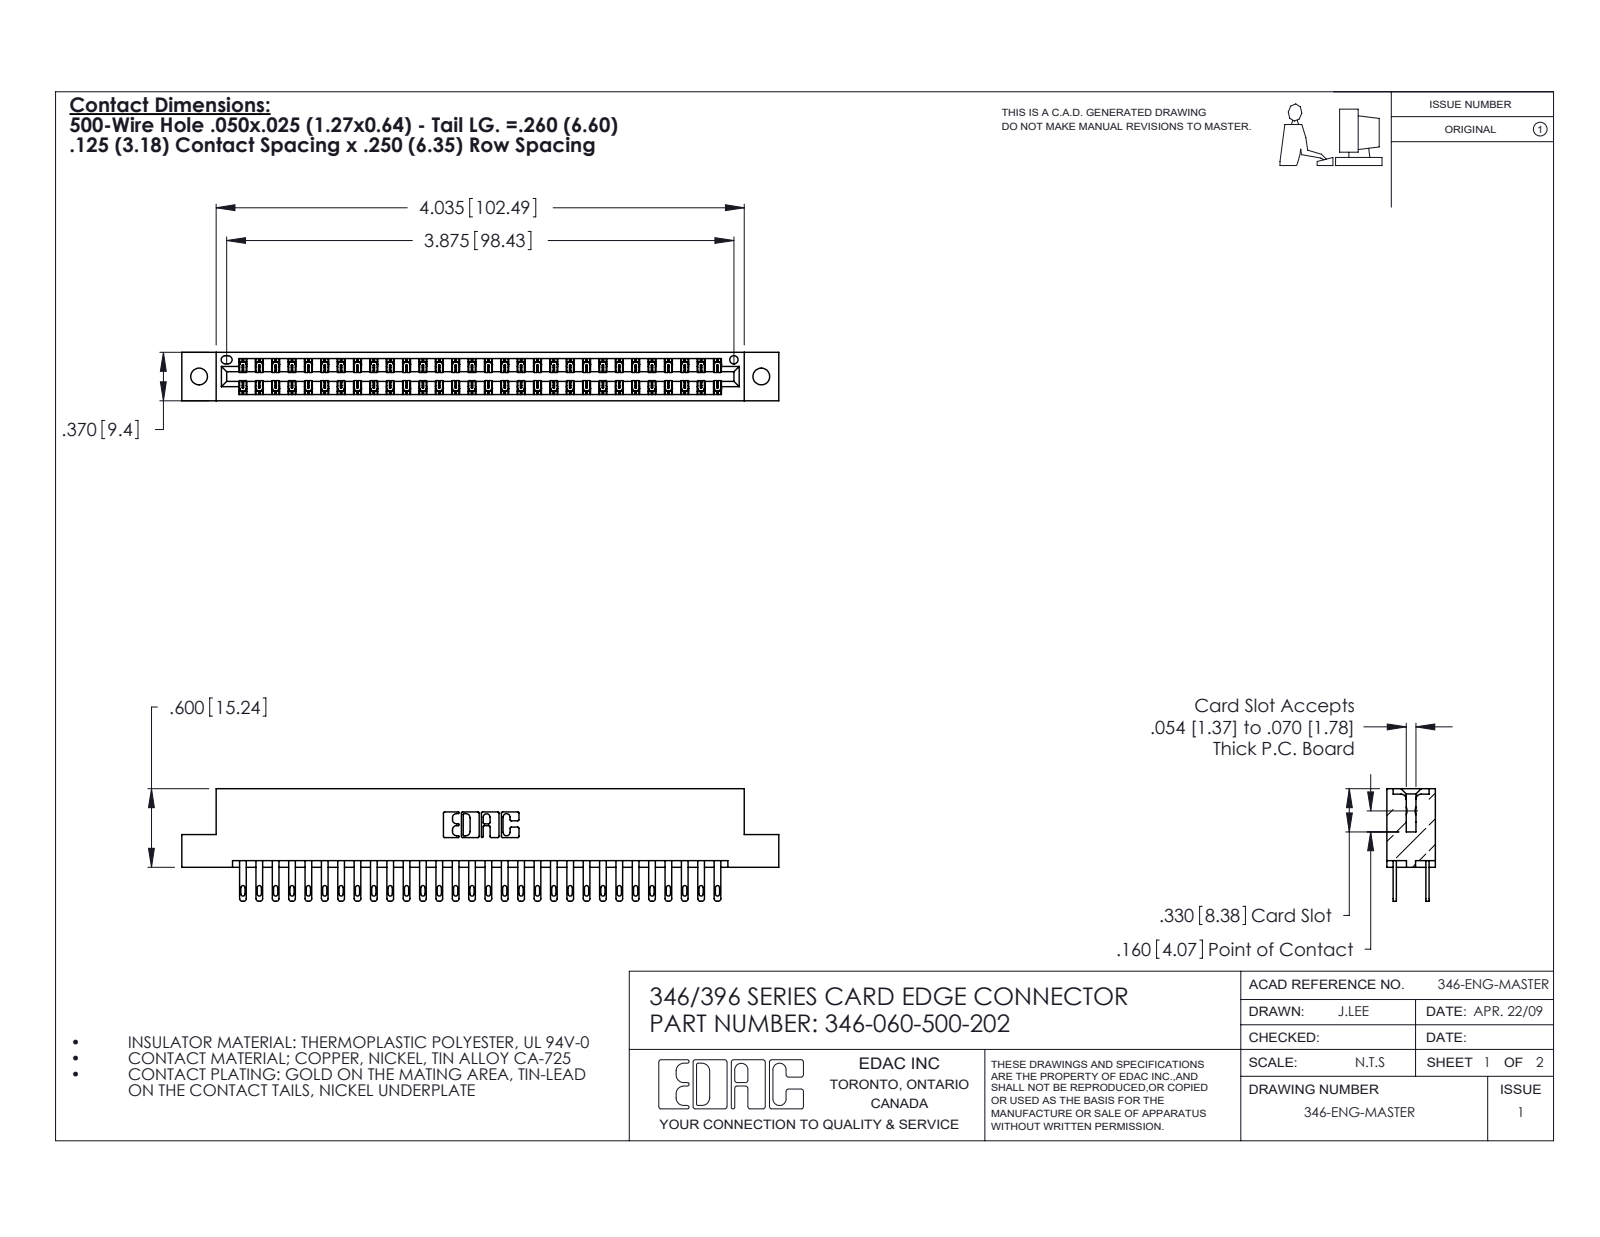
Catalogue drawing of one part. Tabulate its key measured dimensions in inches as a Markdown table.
| quantity | value |
| --- | --- |
| part name | 345-292-001_345-293-100; 346 Part_Flush Mounting Lugs - 0.128 Dia; 346-060-500-202 |
| STEP written by | SolidWorks 2020 (CONFIG_CONTROL_DESIGN) |
| units | inches |
| bodies | 61 solids, 3002 faces (1816 planar, 1186 cylindrical, 0 other) |
| overall size | 4.56 × 0.86 × 0.37 |
| volume | 0.692 in³ |
| surface area | 24.44 in² |
| round holes (diameter × count) | 0.128 × 2, 0.064 × 1 |
| partial cylindrical surfaces (radius × count) | 0.006 × 90, 0.016 × 60, 0.02 × 60, 0.01 × 22, 0.007 × 6, 0.031 × 6, 0.026 × 3, 0.014 × 2 |
| main face-to-face distances | 0.048, 0.322, 0.25, 0.37, 0.072, 0.298, 0.025, 0.275, 0.148, 0.222 |
| hole center spacings | 0.246, 4.087, 4.295 |
